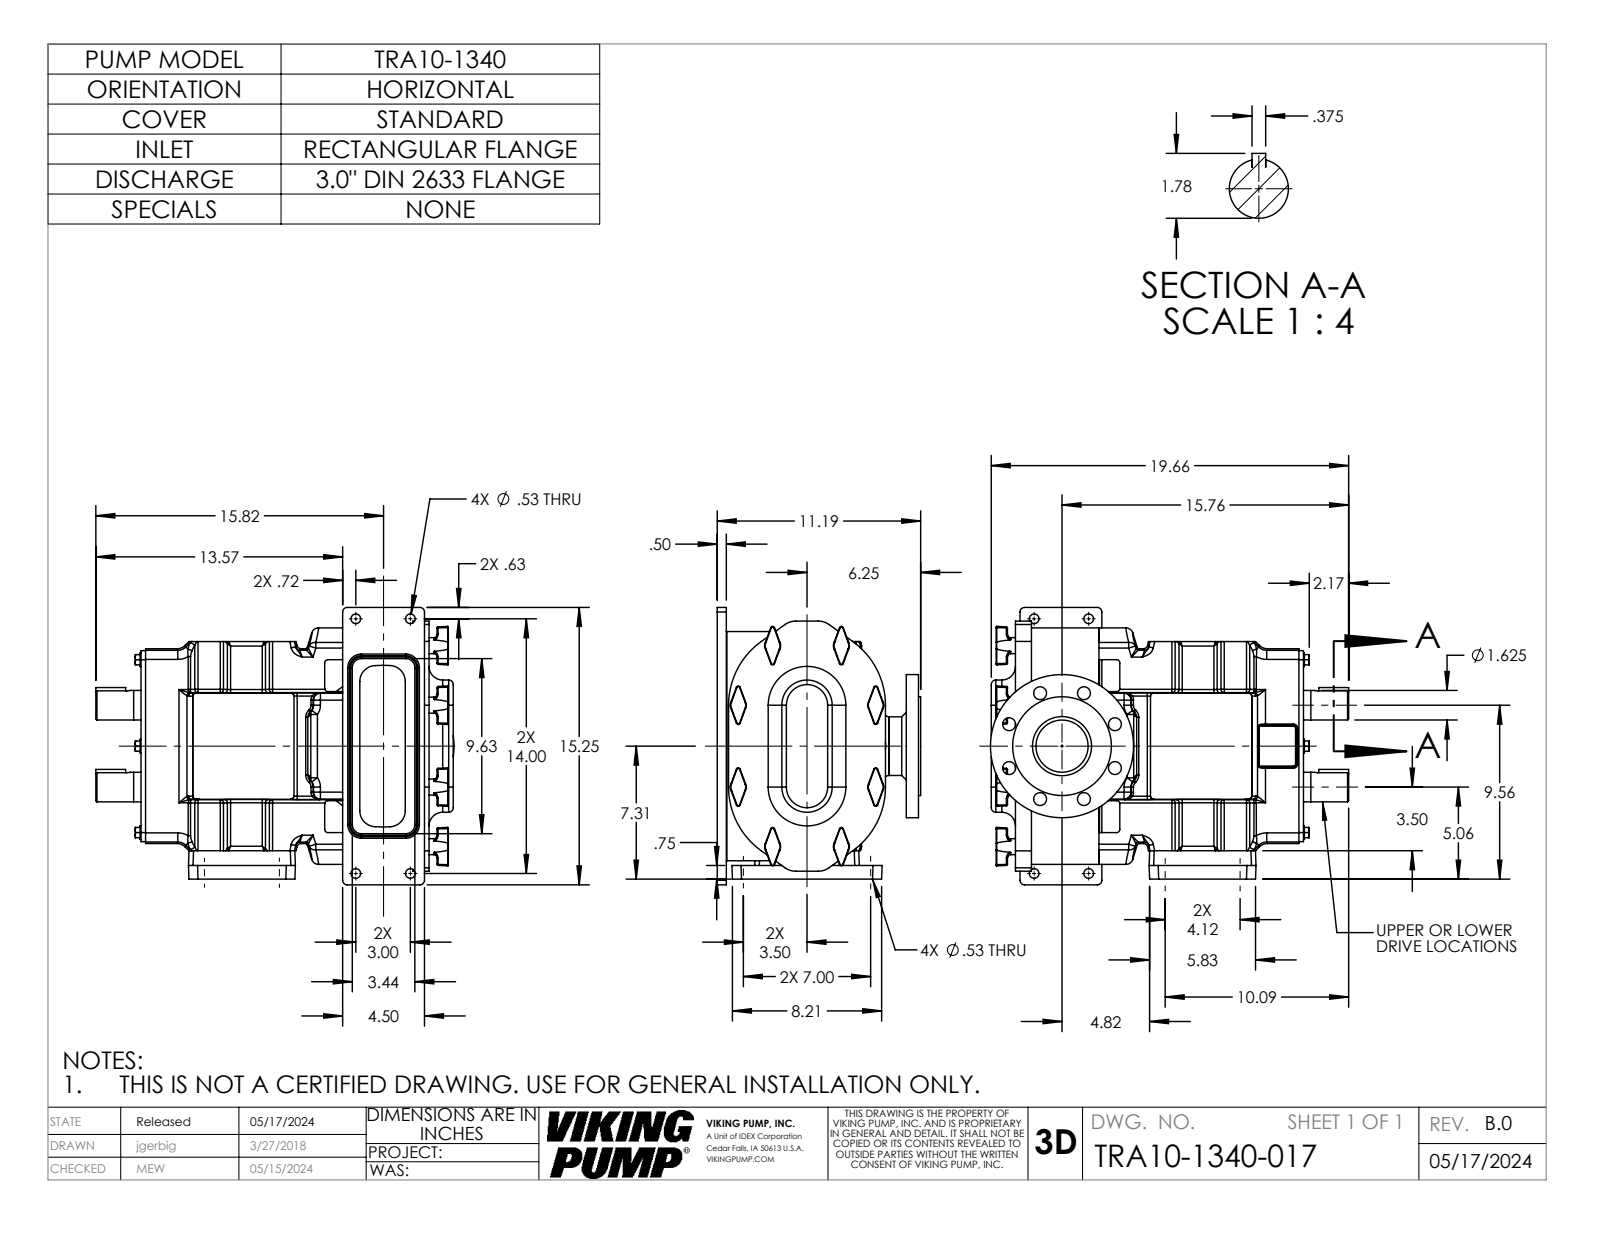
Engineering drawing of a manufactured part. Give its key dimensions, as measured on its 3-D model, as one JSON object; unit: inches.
{"part_name": "TRA10-0600-GEARBOX-H; TRA10-1340-BODY; TRA10-0600-COVER-STD; TRA10-1340-017 (+1 more)", "step_written_by": "SolidWorks 2023 (AUTOMOTIVE_DESIGN)", "units": "inches", "bodies": {"solids": 4, "faces": 1102, "planar": 303, "cylindrical": 417, "other": 382}, "overall_size": [19.699, 15.25, 11.188], "volume_in3": 1361, "surface_area_in2": 1568, "round_holes": [[0.531, 8], [0.709, 8], [2.868, 1], [3.25, 1]], "round_bosses_or_shafts": [[0.88, 8], [0.75, 6], [1.624, 2], [7.87, 1], [5.43, 1], [3.224, 1]], "partial_cylinders_radius": [[0.18, 44], [0.06, 43], [0.03, 36], [0.25, 36], [0.38, 28], [0.5, 26], [0.12, 24], [0.09, 16]], "face_to_face_distances": [3.711, 0.5, 0.88, 4.591, 0.36, 15.841, 14.961, 11.25, 6.5, 1.437], "hole_center_spacings": [3.15, 4.454, 5.82, 2.411, 6.299, 2.41, 2.411, 3]}
